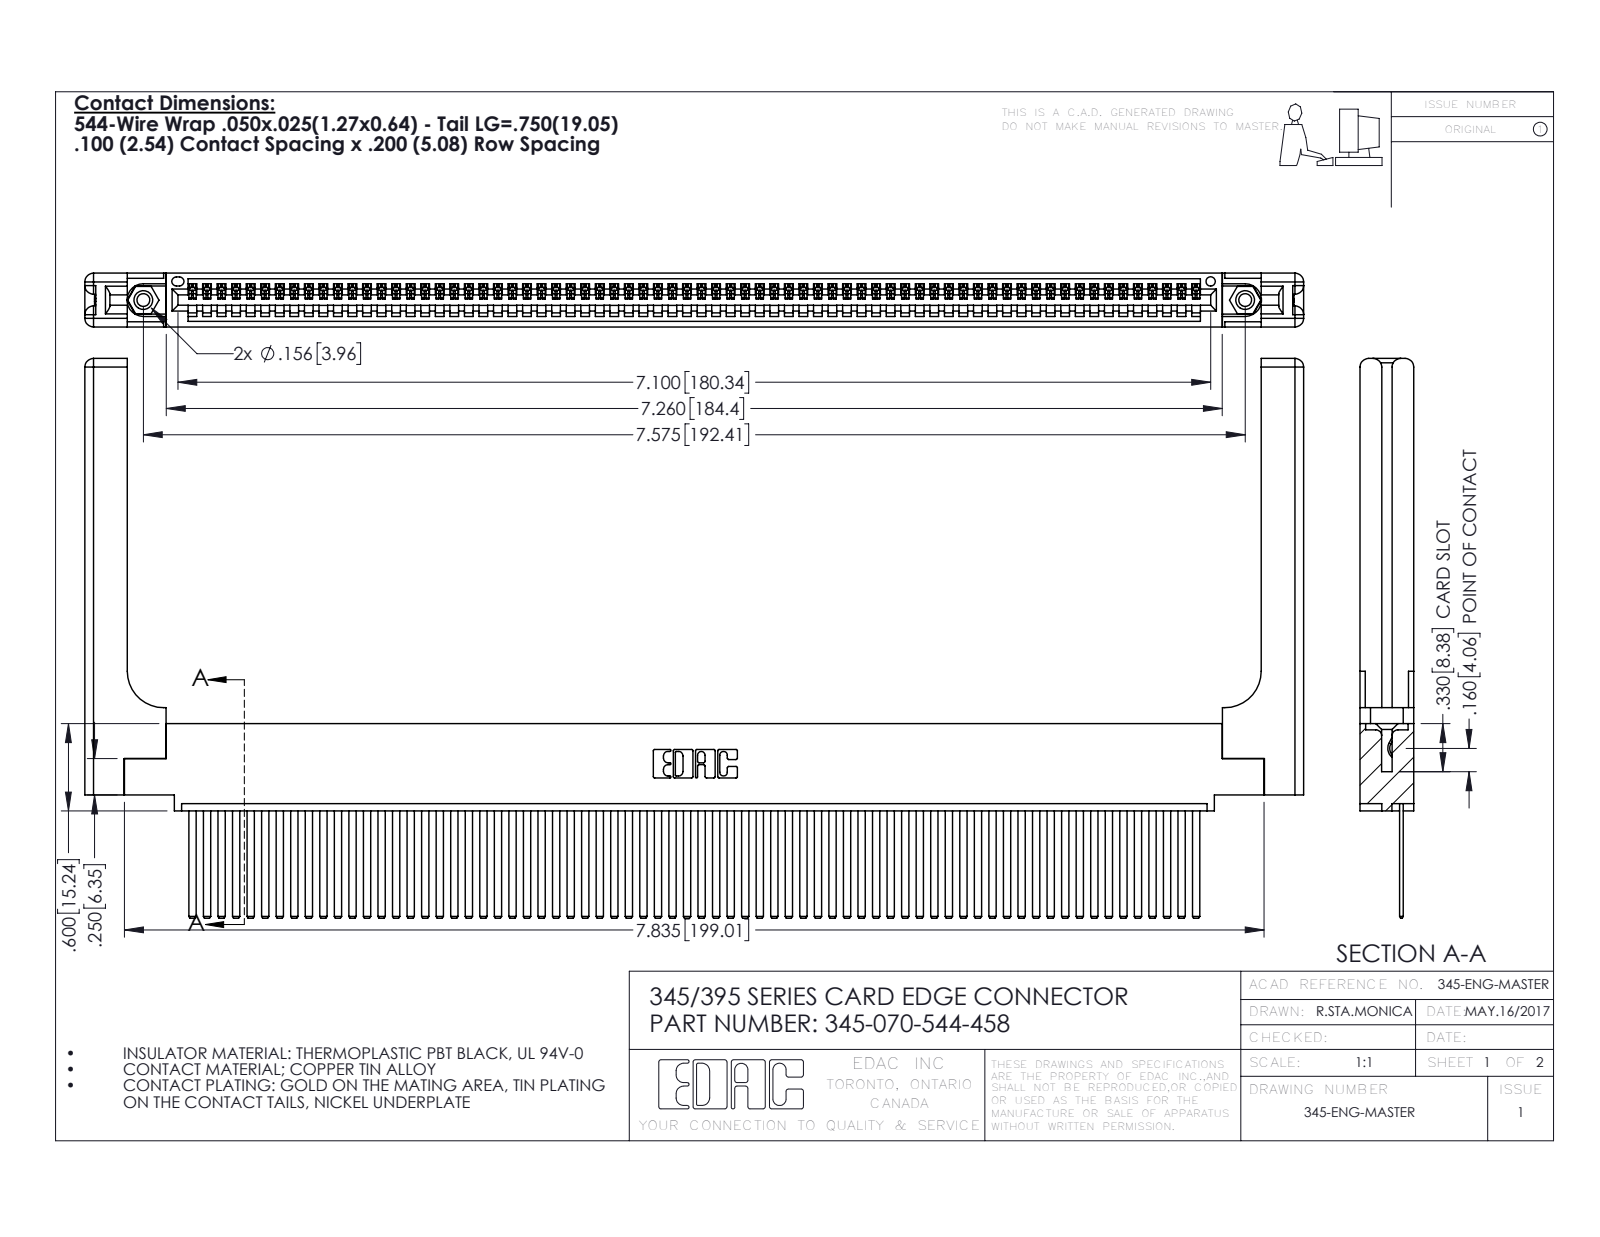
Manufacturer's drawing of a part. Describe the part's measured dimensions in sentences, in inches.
The part is named "345-250-001_345-250-001-102; 345-220-058_345-220-058; 345 Part_0.110 Offset - 0.156 Dia-TH; 345-292-001_345-293-144 (+1 more)". Its 3-D file was written by "SolidWorks 2016 (CONFIG_CONTROL_DESIGN)". It is 75 solids with 4026 faces: 2752 planar, 1214 cylindrical and 60 other. Overall it measures 8.379 by 3.847 by 0.37 inches. Its volume is 1.812 cubic inches and its surface area 56.34 square inches. Round holes: 2 of diameter 0.089, 2 of diameter 0.125, 2 of diameter 0.156, 1 of diameter 0.064. Round bosses or shafts: 2 of diameter 0.155. Partial cylindrical surfaces (rounded edges, fillets, slot ends): 140 of radius 0.006, 22 of radius 0.01, 16 of radius 0.06, 6 of radius 0.007, 6 of radius 0.031, 3 of radius 0.026, 2 of radius 0.03, 2 of radius 0.031. The main face-to-face distances are 0.072, 0.298, 0.098, 0.272, 0.025, 0.37, 0.2, 0.225, 0.148, 0.15. The hole center spacings are 0.27, 7.339, 7.575.
